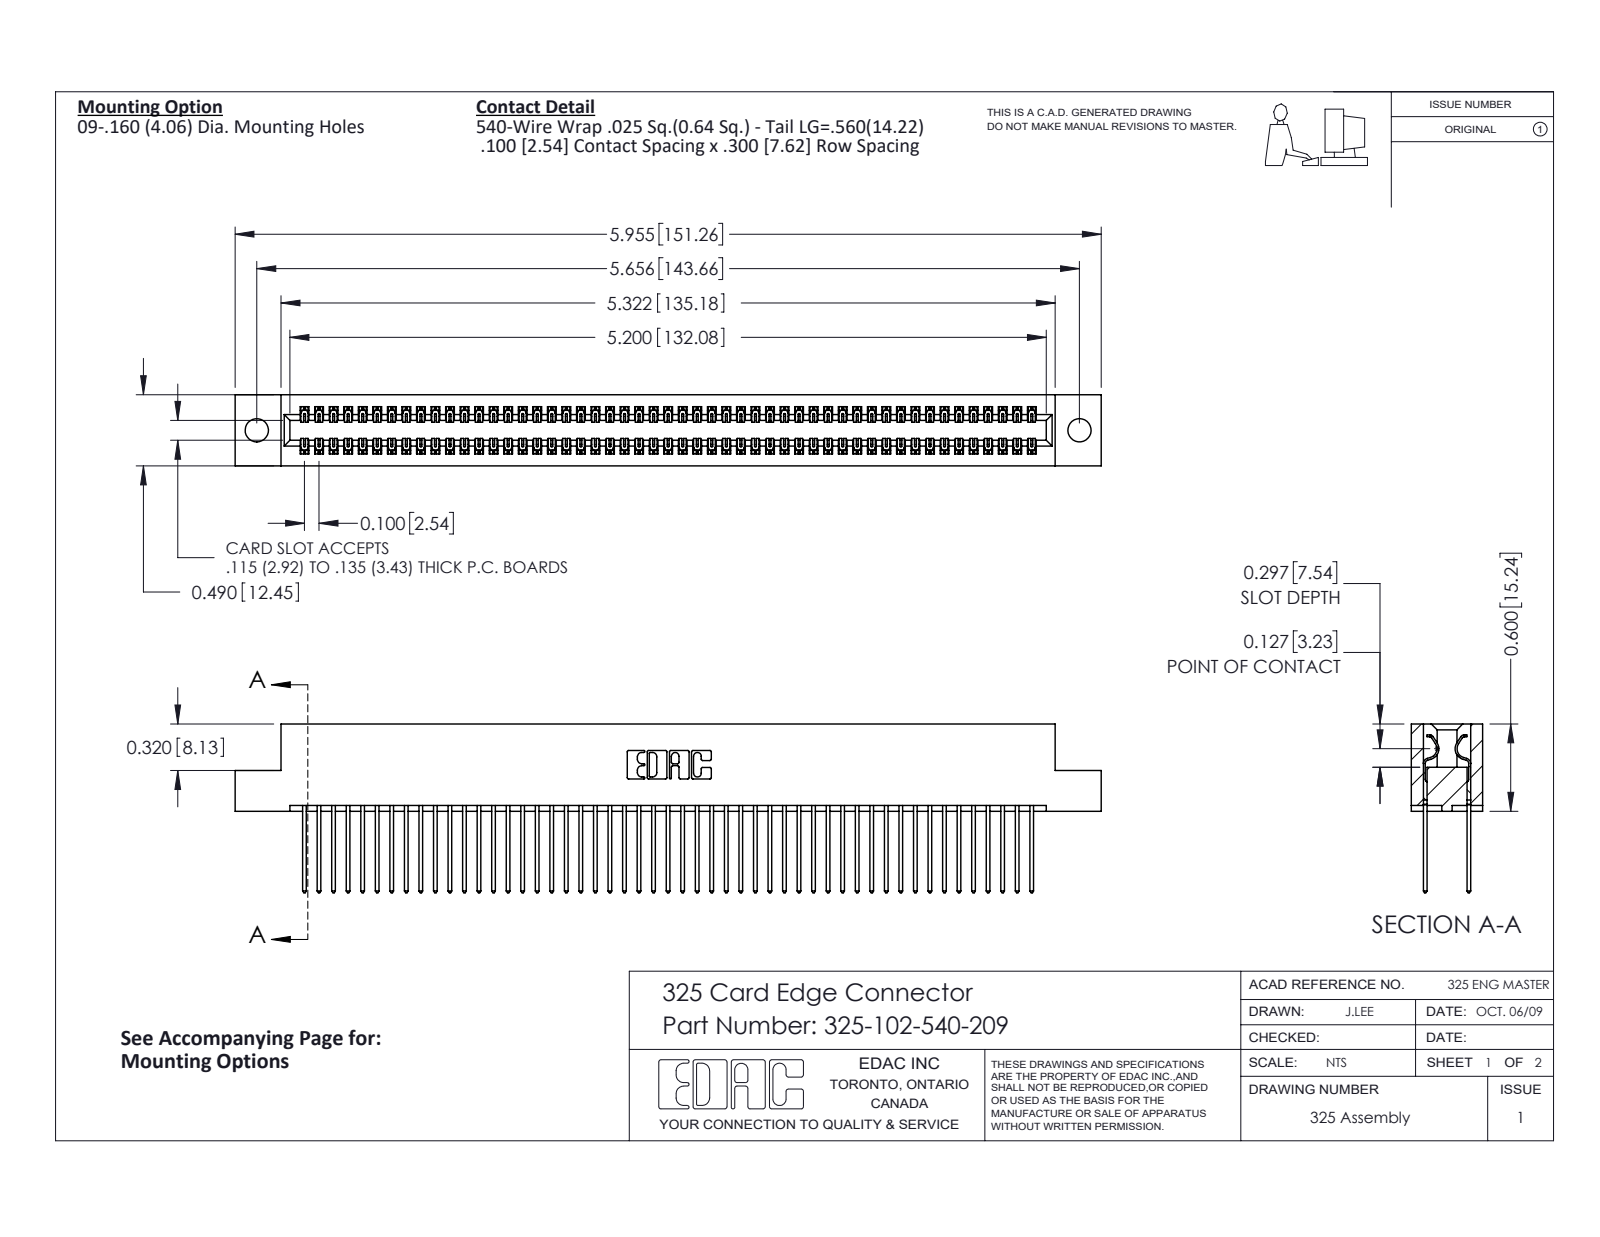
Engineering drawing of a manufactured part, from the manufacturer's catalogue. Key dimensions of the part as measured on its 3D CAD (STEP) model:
Part name (STEP PRODUCT): 325-102-540-209; 325 Part_.160 TH; 325-292-001_325-293-140
STEP written by: SolidWorks 2016 (CONFIG_CONTROL_DESIGN)
Units: inches
Bodies: 103 solids, 5418 faces (3742 planar, 1676 cylindrical, 0 other)
Overall size (bounding box): 5.955 × 1.16 × 0.49
Volume: 1.206 in³ · Surface area: 40.14 in²
Round holes (diameter × count): ⌀0.16 ×2
Partial cylindrical surfaces — rounded edges, fillets, slot ends (radius × count): R0.006 ×153, R0.01 ×102, R0.01 ×22, R0.007 ×6, R0.031 ×6, R0.026 ×3, R0.014 ×2, R0.022 ×2
Main face-to-face distances: 0.083, 0.407, 0.3, 0.107, 0.383, 0.025, 0.325, 0.49, 0.275, 0.56
Hole centre spacings: 5.656
